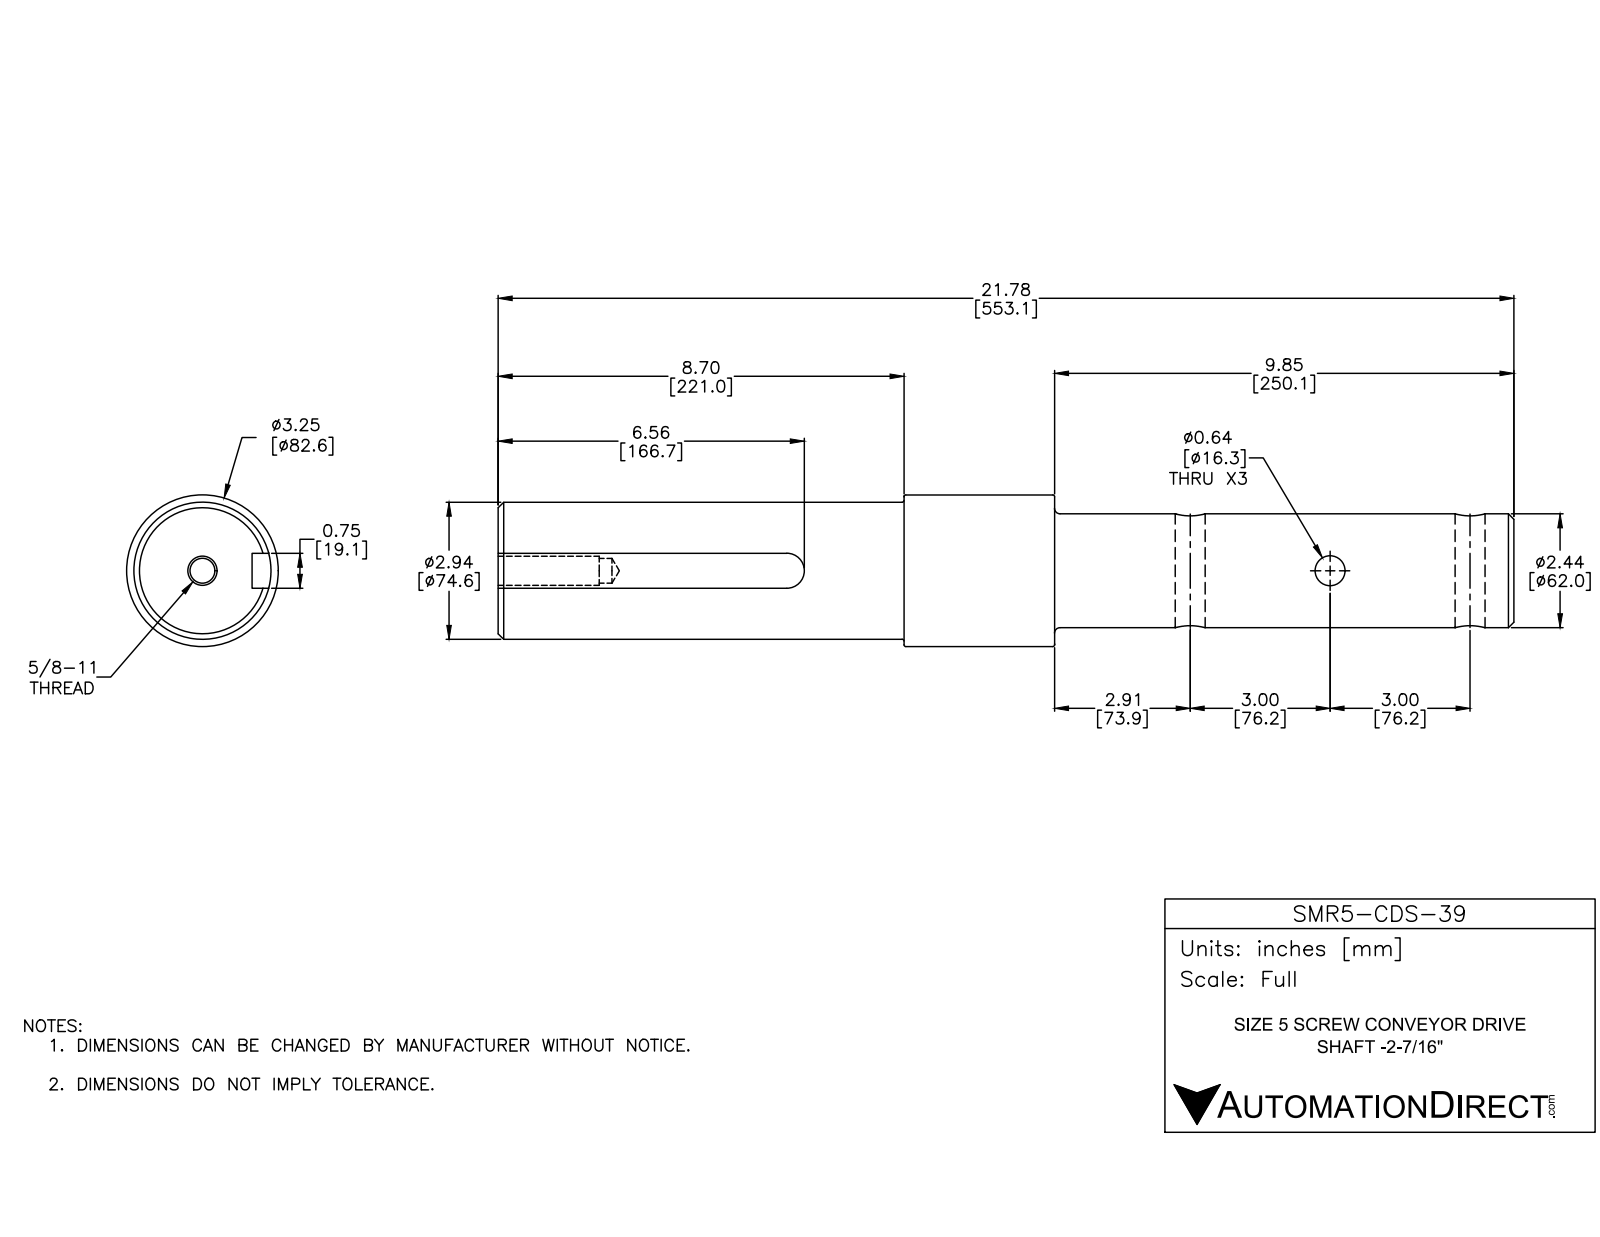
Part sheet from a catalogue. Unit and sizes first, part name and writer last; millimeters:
Units: millimetres
Overall size (bounding box): 553.1 × 82.6 × 82.6
Round holes (diameter × count): ⌀16.3 ×3, ⌀13.5 ×1, ⌀15.9 ×1
Round bosses / shafts (diameter × count): ⌀82.6 ×1, ⌀74.6 ×1, ⌀62 ×1
Partial cylindrical surfaces — rounded edges, fillets, slot ends (radius × count): R9.5 ×1
Main face-to-face distances: 553.1, 303, 250.1, 19.1, 221, 82, 332.1, 55, 166, 248
Hole centre spacings: 152.4
Volume: 2 076 000 mm³ · Surface area: 145 200 mm²
Bodies: 1 solid, 40 faces (8 planar, 18 cylindrical, 14 other)
Part name (STEP PRODUCT): SMR5-CDS-39
STEP written by: SolidWorks 2016 (AUTOMOTIVE_DESIGN)
